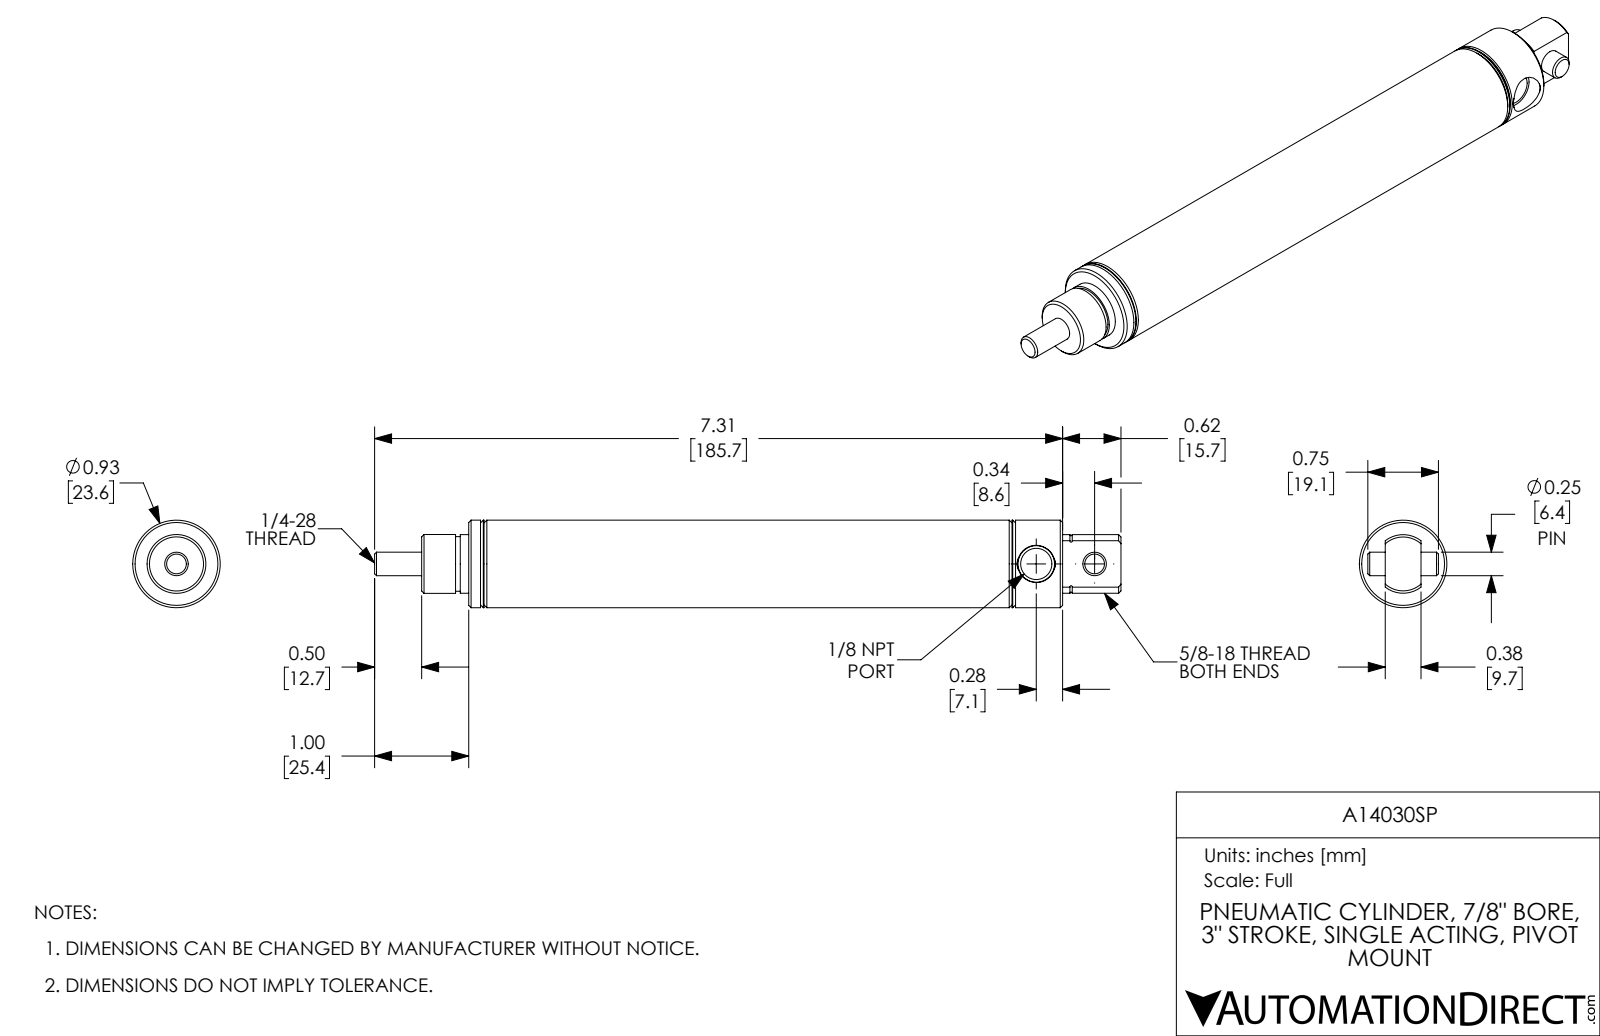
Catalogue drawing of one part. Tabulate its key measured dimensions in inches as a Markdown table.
| quantity | value |
| --- | --- |
| part name | A14030SP-Pin; A14030SP; A14030SP-MainBody; A14030SP-Rod |
| STEP written by | SolidWorks 2017 (AUTOMOTIVE_DESIGN) |
| units | inches |
| bodies | 3 solids, 87 faces (20 planar, 34 cylindrical, 33 other) |
| overall size | 7.93 × 0.93 × 0.93 |
| volume | 2.919 in³ |
| surface area | 42.25 in² |
| round holes (diameter × count) | 0.25 × 2, 0.332 × 1, 0.875 × 1 |
| round bosses / shafts (diameter × count) | 0.93 × 1, 0.625 × 1, 0.623 × 1, 0.58 × 1 |
| main face-to-face distances | 0.5, 3.5, 3, 4.717, 1.593, 6.31, 2.093, 5.093, 4.217, 1.217 |
| hole center spacings | 0.62 |
